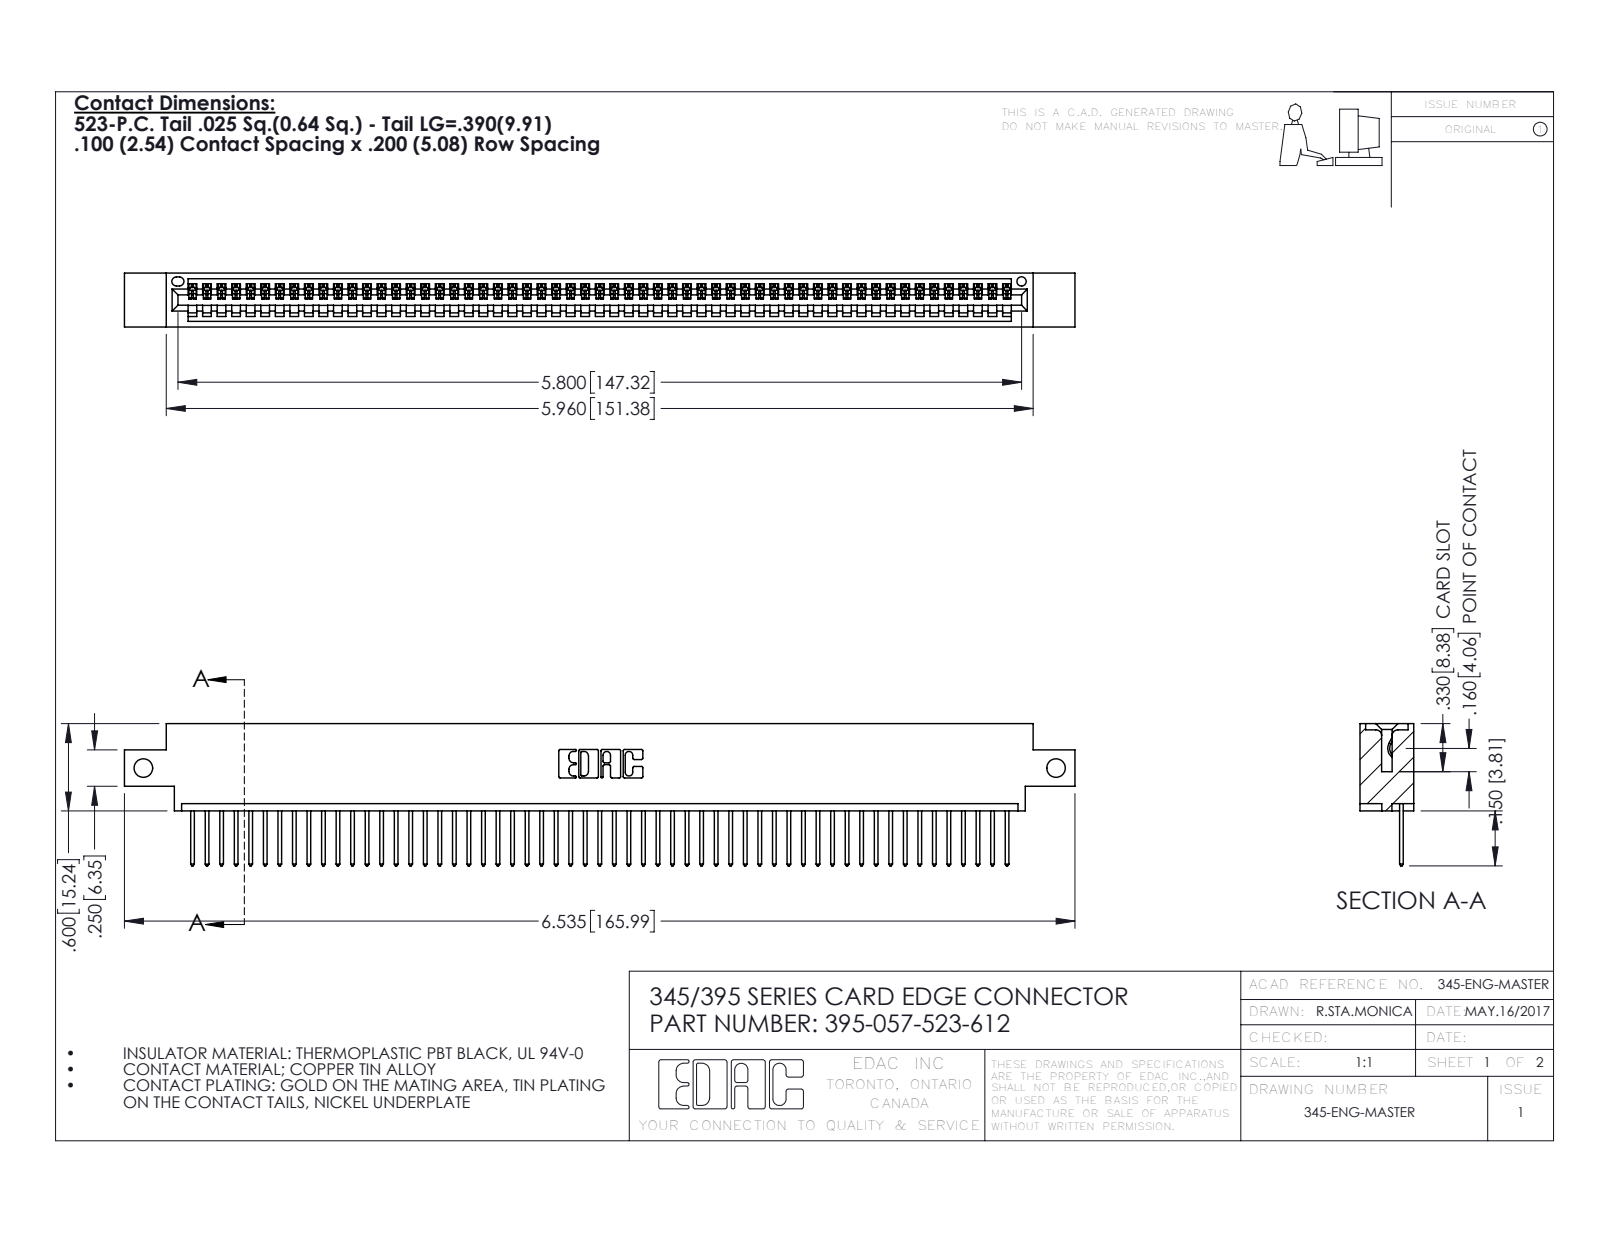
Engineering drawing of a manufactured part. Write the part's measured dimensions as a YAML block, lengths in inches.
part_name: "395-057-523-612; 345-292-001_345-293-123; 345 Part_0.170 Offset - Side Mount"
step_written_by: "SolidWorks 2016 (CONFIG_CONTROL_DESIGN)"
units: inches
bodies: {solids: 58, faces: 3436, planar: 2364, cylindrical: 1072, other: 0}
overall_size: [6.535, 0.977, 0.37]
volume: 0.956
surface_area: 32.66
round_holes:
  - {diameter: 0.128, count: 2}
  - {diameter: 0.064, count: 1}
partial_cylinders:
  - {radius: 0.006, count: 114}
  - {radius: 0.01, count: 114}
  - {radius: 0.01, count: 22}
  - {radius: 0.007, count: 6}
  - {radius: 0.031, count: 6}
  - {radius: 0.026, count: 3}
  - {radius: 0.031, count: 2}
  - {radius: 0.04, count: 2}
face_to_face_distances: [0.298, 0.072, 0.37, 0.098, 0.272, 0.025, 0.2, 0.225, 0.175, 0.149]
hole_center_spacings: [6.275]
